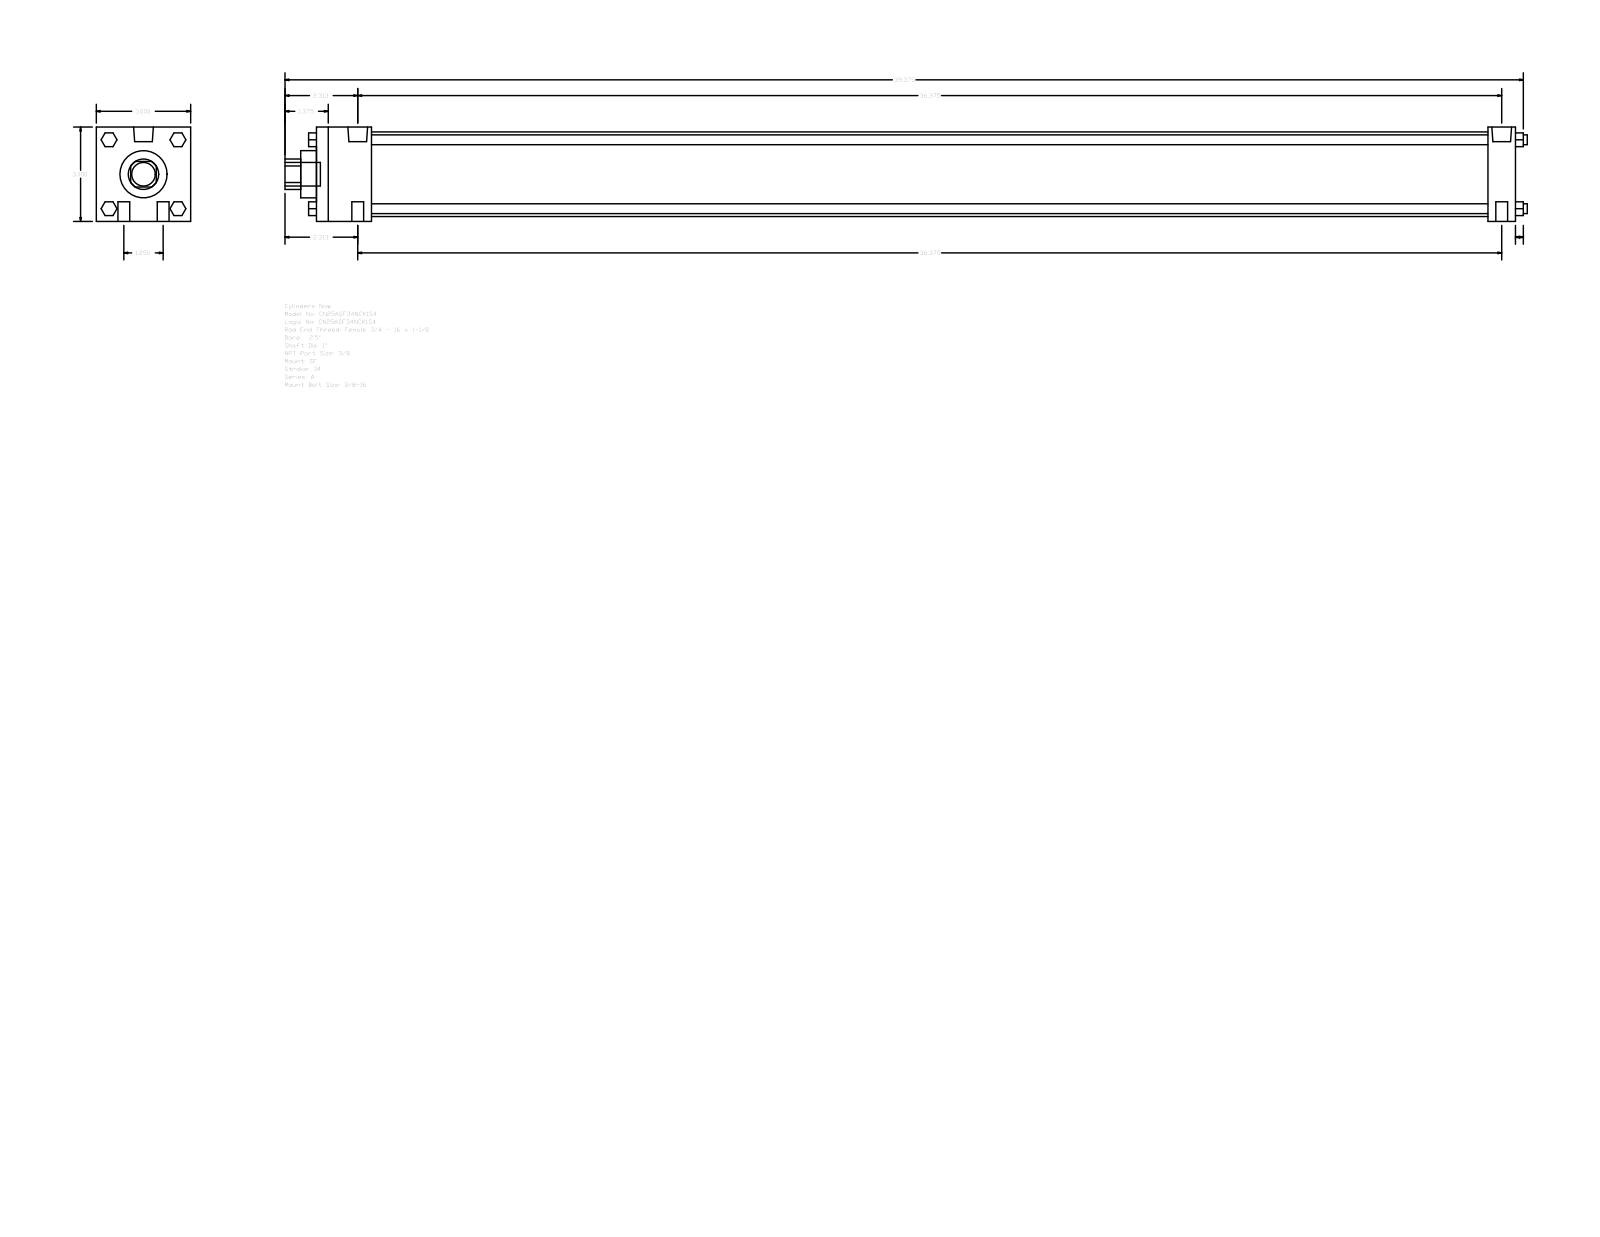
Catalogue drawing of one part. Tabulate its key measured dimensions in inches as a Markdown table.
| quantity | value |
| --- | --- |
| part name | A_SF__0250_1 |
| STEP written by | GSSL Pune (CONFIG_CONTROL_DESIGN) |
| units | inches |
| bodies | 0 solids, 124 faces (94 planar, 30 cylindrical, 0 other) |
| overall size | 39.5 × 3 × 3 |
| round holes (diameter × count) | 1 × 1, 1.5 × 1, 2.69 × 1 |
| round bosses / shafts (diameter × count) | 0.375 × 4, 0.313 × 4, 0.627 × 2, 0.219 × 2, 0.75 × 1 |
| partial cylindrical surfaces (radius × count) | 0.484 × 1 |
| main face-to-face distances | 3, 38.125, 37.25, 0.875, 1.75, 35.5, 36.375, 0.5, 38.625, 0.25 |
